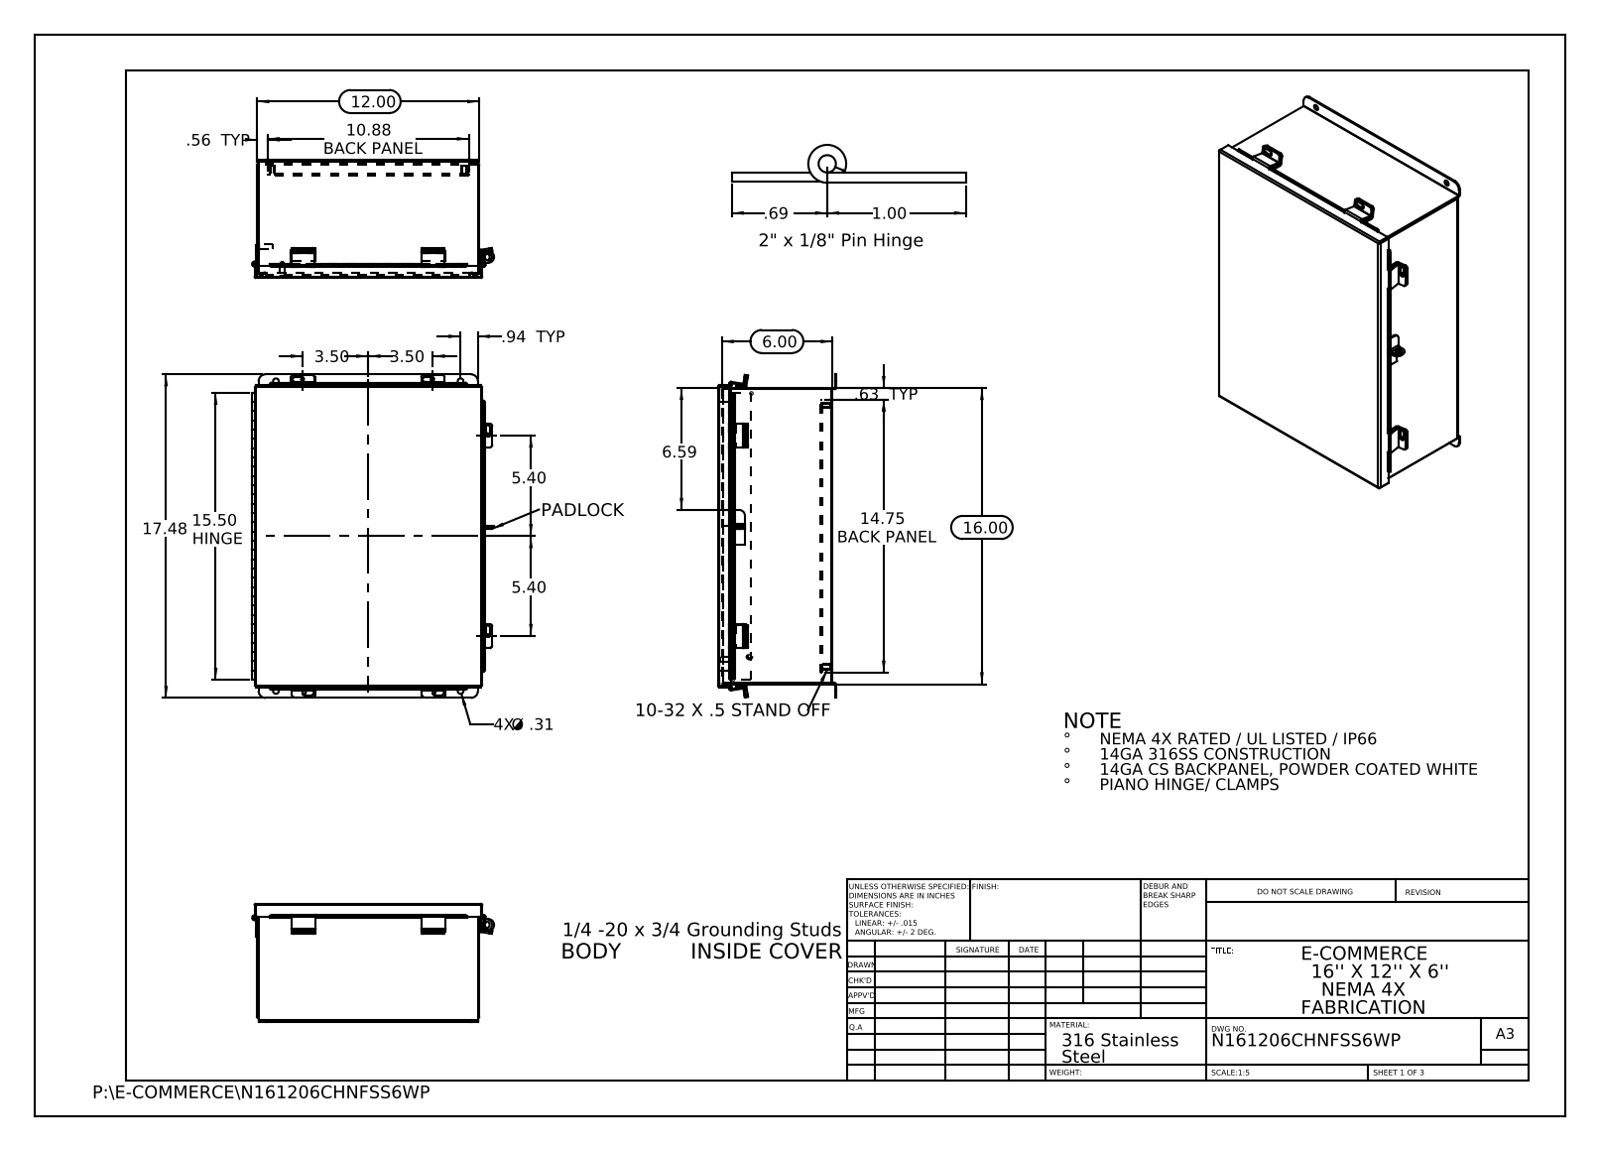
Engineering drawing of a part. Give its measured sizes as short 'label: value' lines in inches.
name: HW-CLH-JH-20154; N161206CHNFSS6WP JIC Enclosure Template; N161206CHNFSS6WP; HW-CLH-JH-20104 (+8 more)
written by: SolidWorks 2013 (CONFIG_CONTROL_DESIGN)
unit: in
bodies: 27 solids, 866 faces (539 planar, 307 cylindrical, 20 other)
size: 17.476 × 13.072 × 6.39
volume: 75.45 in³; area: 2 054 in²
holes: 10× ⌀0.25, 4× ⌀0.187, 4× ⌀0.312, 1× ⌀0.125, 1× ⌀0.125, 1× ⌀0.373, 1× ⌀0.375
bosses: 4× ⌀0.313, 2× ⌀0.315, 2× ⌀0.236, 1× ⌀0.273, 1× ⌀0.25
rounds: 22× R0.125, 13× R0.013, 12× R0.009, 12× R0.088, 12× R0.133, 6× R0.083, 6× R0.1, 4× R0.375
face distances: 0.075, 6.128, 6.053, 6.203, 11.925, 0.074, 5.628, 0.575, 0.5, 5.553
hole spacings: 1.315, 10.258, 15.427, 18.48, 7, 9.976, 10.375, 14.126
